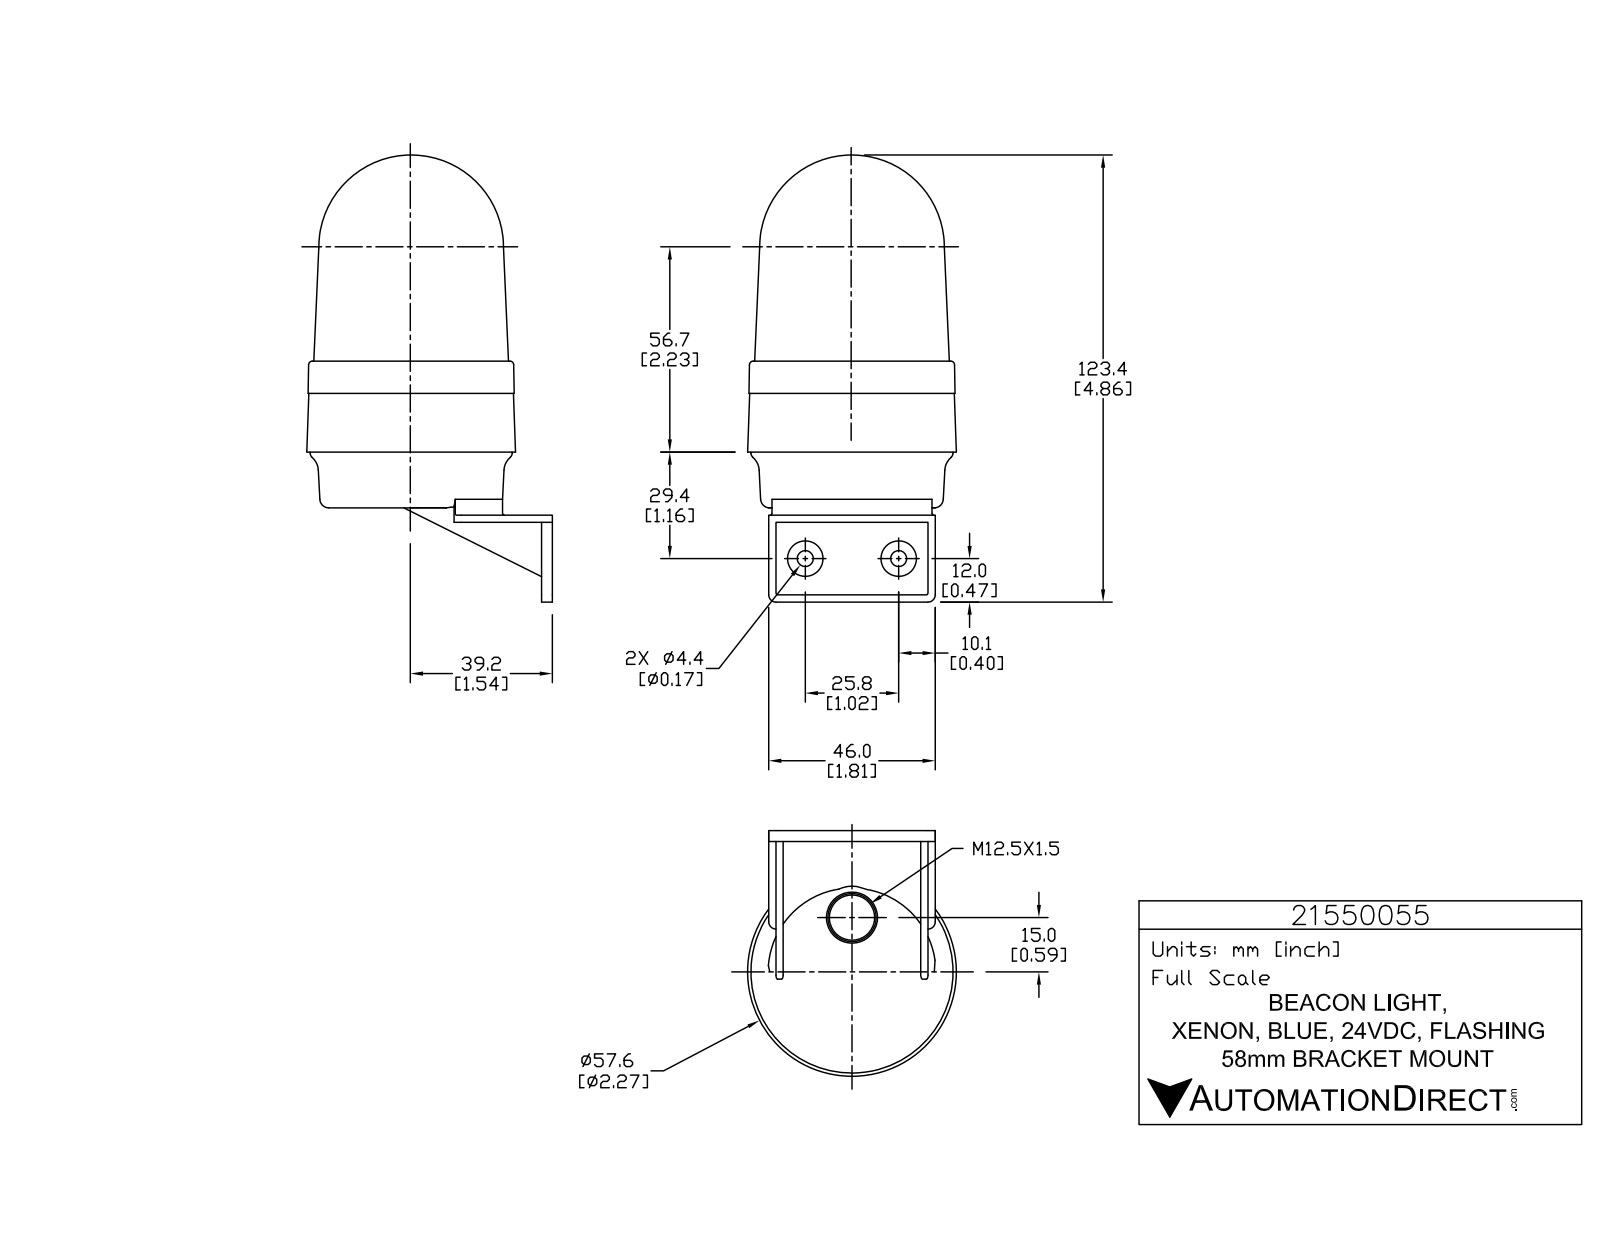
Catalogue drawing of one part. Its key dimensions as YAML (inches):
part_name: "21550055"
step_written_by: "SolidWorks 2015 (AUTOMOTIVE_DESIGN)"
units: inches
bodies: {solids: 1, faces: 828, planar: 551, cylindrical: 179, other: 98}
overall_size: [4.858, 2.852, 2.407]
volume: 12.43
surface_area: 37.49
round_holes:
  - {diameter: 0.039, count: 3}
  - {diameter: 0.173, count: 2}
round_bosses_or_shafts:
  - {diameter: 0.226, count: 3}
  - {diameter: 0.056, count: 3}
  - {diameter: 0.386, count: 2}
  - {diameter: 2.197, count: 1}
partial_cylinders:
  - {radius: 0.008, count: 6}
  - {radius: 0.008, count: 6}
  - {radius: 0.008, count: 6}
  - {radius: 0.02, count: 6}
  - {radius: 0.131, count: 6}
  - {radius: 0.079, count: 4}
  - {radius: 0.004, count: 3}
  - {radius: 0.005, count: 3}
face_to_face_distances: [0.079, 0.157, 1.575, 1.654, 0.039, 0.118, 1.496, 0.866, 0.945, 0.764]
hole_center_spacings: [1.016]
